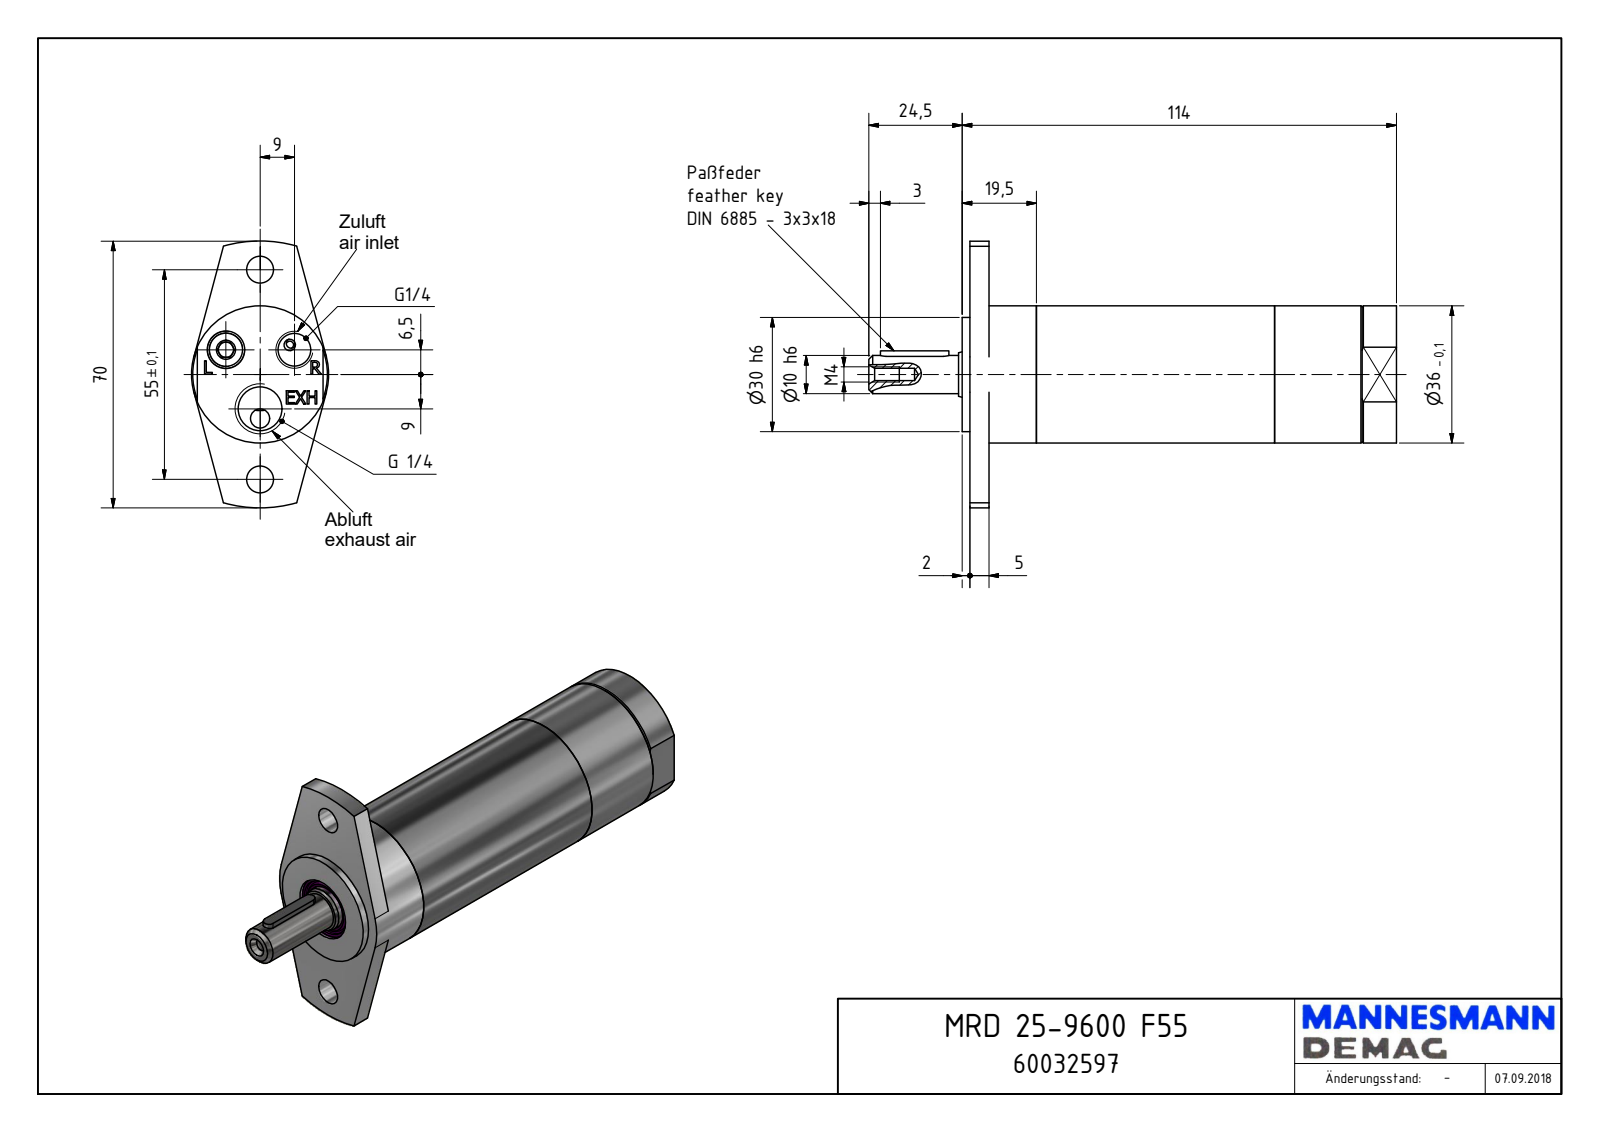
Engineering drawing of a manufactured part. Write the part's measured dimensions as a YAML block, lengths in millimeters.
part_name: "MRD 25-9600 F55_60032597"
step_written_by: "Autodesk Inventor 2018 (AUTOMOTIVE_DESIGN)"
units: millimeters
bodies: {solids: 1, faces: 141, planar: 96, cylindrical: 21, other: 24}
overall_size: [138.5, 70, 36]
volume: 118790
surface_area: 19382
round_holes:
  - {diameter: 7, count: 2}
  - {diameter: 8.57, count: 2}
  - {diameter: 3.24, count: 1}
  - {diameter: 4, count: 1}
  - {diameter: 11.45, count: 1}
  - {diameter: 15.5, count: 1}
  - {diameter: 17, count: 1}
round_bosses_or_shafts:
  - {diameter: 36, count: 1}
  - {diameter: 30, count: 1}
  - {diameter: 11.95, count: 1}
  - {diameter: 10, count: 1}
partial_cylinders:
  - {radius: 1.5, count: 2}
  - {radius: 35, count: 1}
face_to_face_distances: [5, 107, 112, 2, 7, 114, 101.95, 99.95, 94.95, 12.05]
hole_center_spacings: [11.1, 17.92, 22.85, 27.5, 35.17, 9, 18, 18.5]
